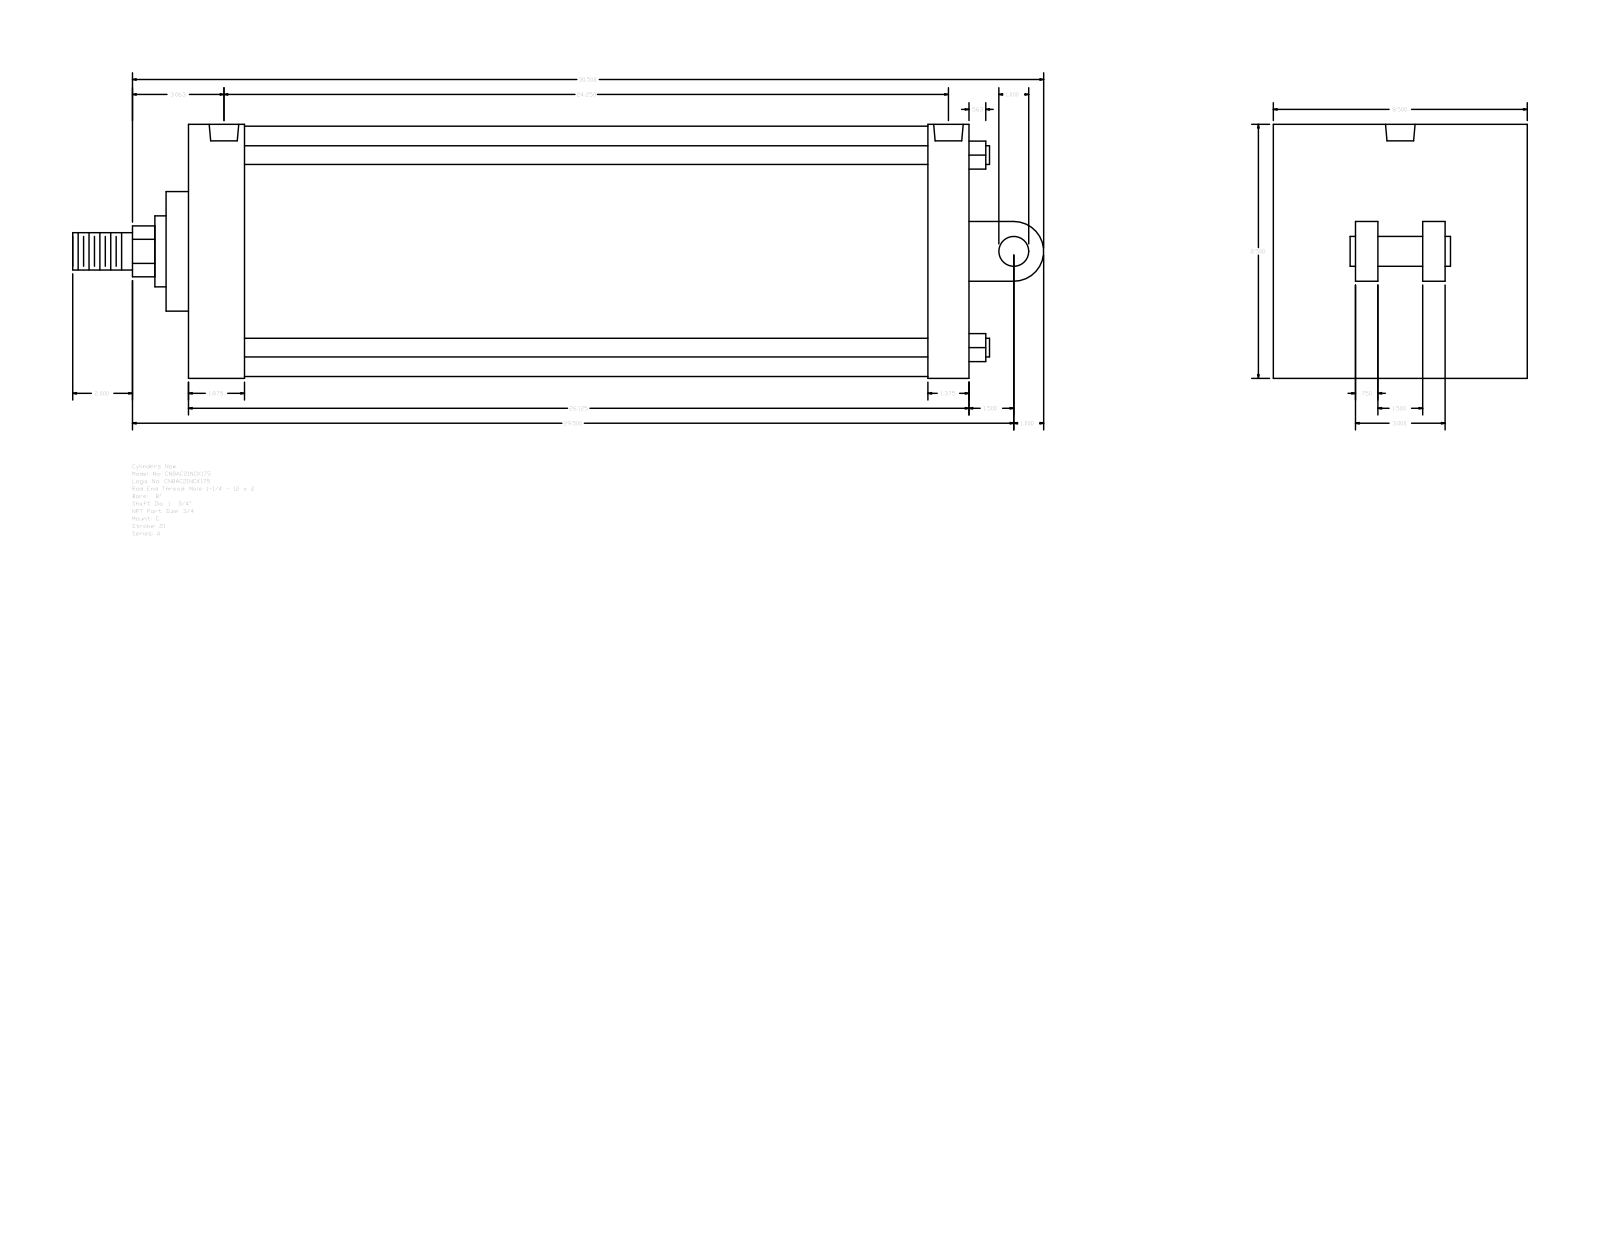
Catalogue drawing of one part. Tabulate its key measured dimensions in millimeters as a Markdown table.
| quantity | value |
| --- | --- |
| part name | A_C__0800_1.75 |
| STEP written by | GSSL Pune (CONFIG_CONTROL_DESIGN) |
| units | millimeters |
| bodies | 0 solids, 104 faces (75 planar, 29 cylindrical, 0 other) |
| overall size | 825.5 × 215.9 × 215.9 |
| round holes (diameter × count) | 15.08 × 4, 25.12 × 2 |
| round bosses / shafts (diameter × count) | 15.88 × 4, 212.72 × 1, 60.33 × 1, 44.45 × 1, 31.75 × 1, 25.4 × 1 |
| partial cylindrical surfaces (radius × count) | 21.63 × 1, 25.4 × 1 |
| main face-to-face distances | 663.58, 215.9, 19.05, 57.15, 47.63, 615.95, 628.65, 581.02, 34.93, 69.85 |
| hole center spacings | 6.35, 603.25, 609.6, 615.95 |
